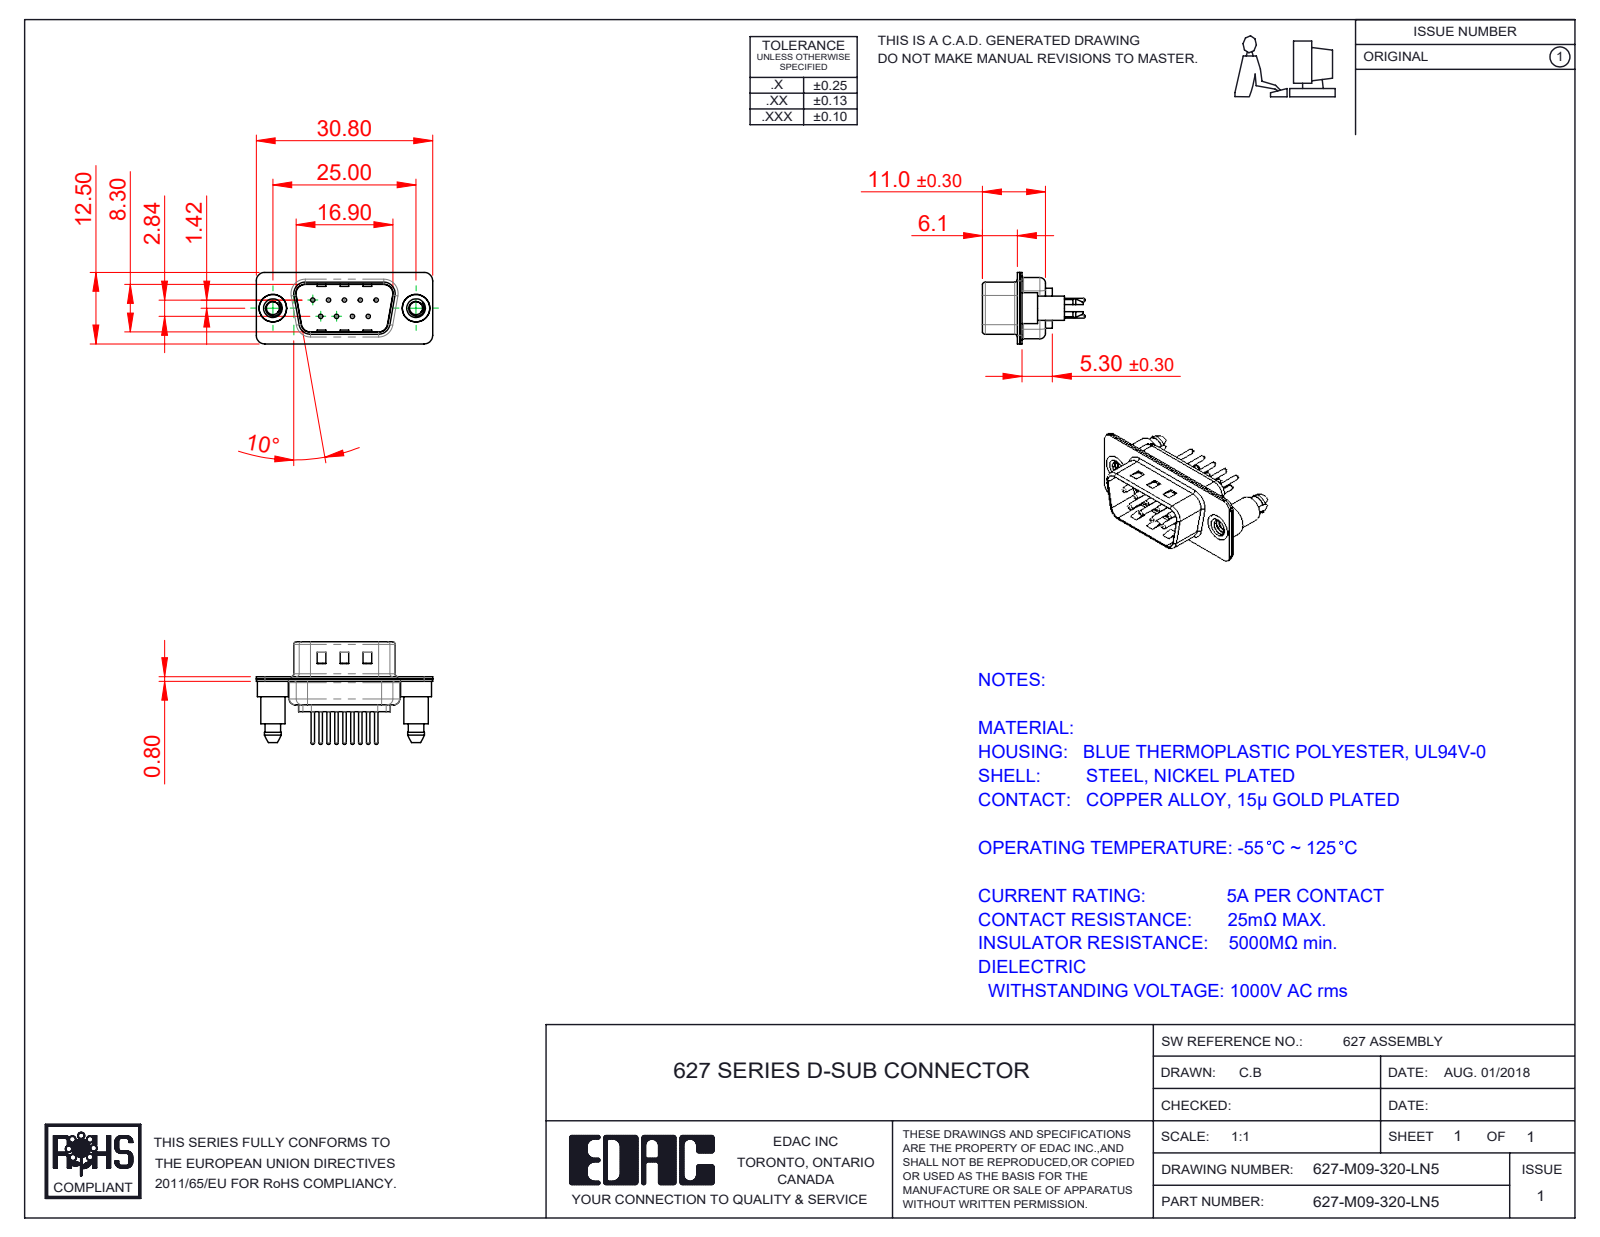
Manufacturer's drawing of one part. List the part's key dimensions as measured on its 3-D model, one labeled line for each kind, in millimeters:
Part name (STEP PRODUCT): 627-M09-320-LN5; 627M Contact Row 2_20; 627M Housing_09 Contacts; 627M Shell Front_09 Contacts (+3 more)
STEP written by: SolidWorks 2020 (CONFIG_CONTROL_DESIGN)
Units: millimetres
Bodies: 14 solids, 687 faces (186 planar, 287 cylindrical, 214 other)
Overall size (bounding box): 30.8 × 17.9 × 12.5
Volume: 1 444 mm³ · Surface area: 3 907 mm²
Round holes (diameter × count): ⌀0.75 ×9, ⌀1.6 ×9, ⌀2 ×9, ⌀2.26 ×2, ⌀4 ×2, ⌀4.8 ×2
Round bosses / shafts (diameter × count): ⌀1.5 ×9, ⌀0.6 ×9, ⌀5.4 ×2, ⌀4.9 ×2, ⌀4.25 ×2
Partial cylindrical surfaces — rounded edges, fillets, slot ends (radius × count): R1.5 ×18, R2 ×12, R1.6 ×10, R0.5 ×8, R0.25 ×4, R0.6 ×4, R0.65 ×4, R0.9 ×4
Main face-to-face distances: 0.4, 0.8, 9.5, 9.1, 8.7, 0.65, 9.9, 1.2, 5.3, 6.1
Hole centre spacings: 3.16, 2.77, 5.54, 5.03, 5.04, 8.31, 7.1, 7.48
